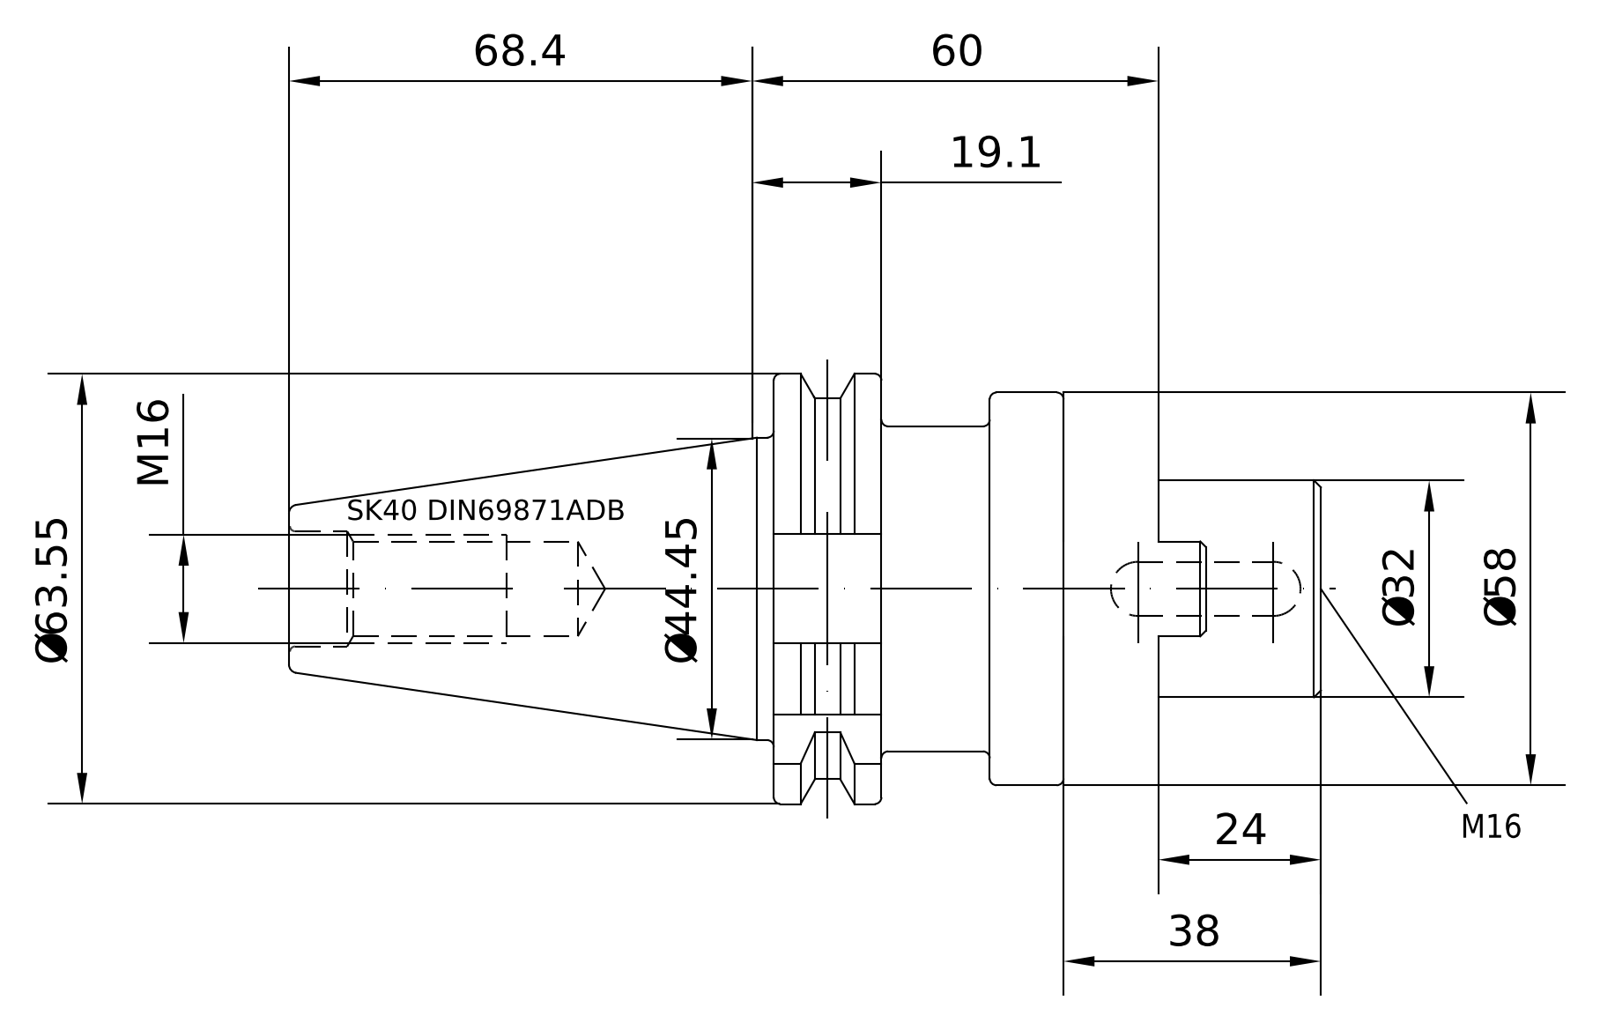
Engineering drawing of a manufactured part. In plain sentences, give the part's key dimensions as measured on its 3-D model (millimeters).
The part is named "40-340-32; 85-200-32; 40-340-32_ASM". Its 3-D file was written by "PRO/ENGINEER BY PARAMETRIC TECHNOLOGY CORPORATION, 2010430 (CONFIG_CONTROL_DESIGN)". It is 2 solids with 197 faces: 90 planar, 45 cylindrical and 62 other. Overall it measures 152.25 by 63.52 by 61.42 millimeters. Its volume is 210 420 cubic millimeters and its surface area 42 549 square millimeters. Round holes: 1 of diameter 13.84, 1 of diameter 14, 1 of diameter 16, 1 of diameter 17.01, 1 of diameter 17.5, 1 of diameter 32.39, 1 of diameter 37. Round bosses or shafts: 1 of diameter 58, 1 of diameter 48, 1 of diameter 43.75, 1 of diameter 32, 1 of diameter 16.01. Partial cylindrical surfaces (rounded edges, fillets, slot ends): 5 of radius 1.35, 2 of radius 4, 1 of radius 7.05, 1 of radius 28, 1 of radius 31.76. The main face-to-face distances are 14, 42.8, 56.8, 15.85, 26.95, 40.95, 80.8, 64.95, 38, 24.
